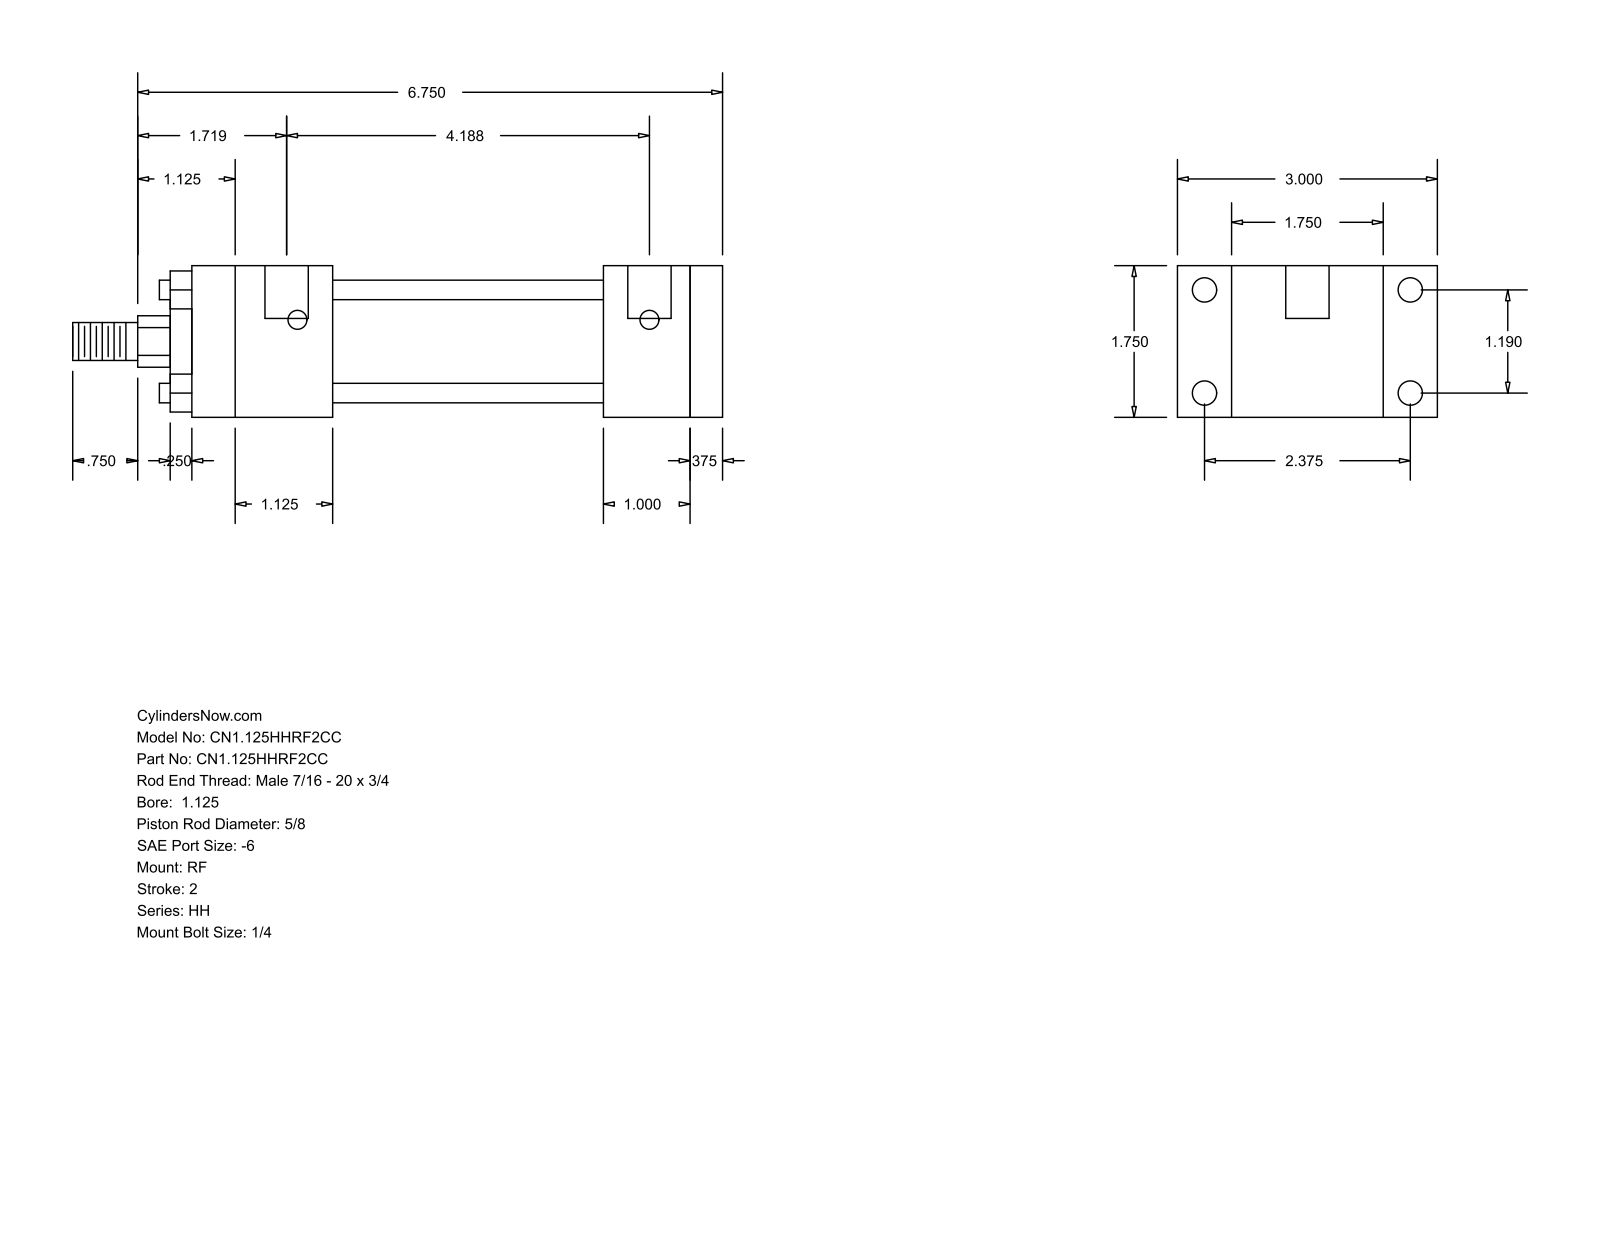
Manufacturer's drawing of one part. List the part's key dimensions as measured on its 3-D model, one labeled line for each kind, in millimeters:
Part name (STEP PRODUCT): HH_RF__0112_0.625
STEP written by: GSSL Pune (CONFIG_CONTROL_DESIGN)
Units: millimetres
Bodies: 0 solids, 92 faces (64 planar, 28 cylindrical, 0 other)
Overall size (bounding box): 190.5 × 76.2 × 44.45
Round holes (diameter × count): ⌀5.56 ×4, ⌀7.14 ×4, ⌀12.7 ×2
Round bosses / shafts (diameter × count): ⌀5.71 ×4, ⌀34.92 ×1, ⌀28.57 ×1, ⌀15.88 ×1, ⌀11.11 ×1
Partial cylindrical surfaces — rounded edges, fillets, slot ends (radius × count): R7.54 ×1
Main face-to-face distances: 44.46, 9.52, 25.4, 15.87, 104.78, 114.3, 79.38, 34.92, 41.27, 120.65
Hole centre spacings: 30.22, 60.32, 67.47, 103.19, 3.17, 106.36
